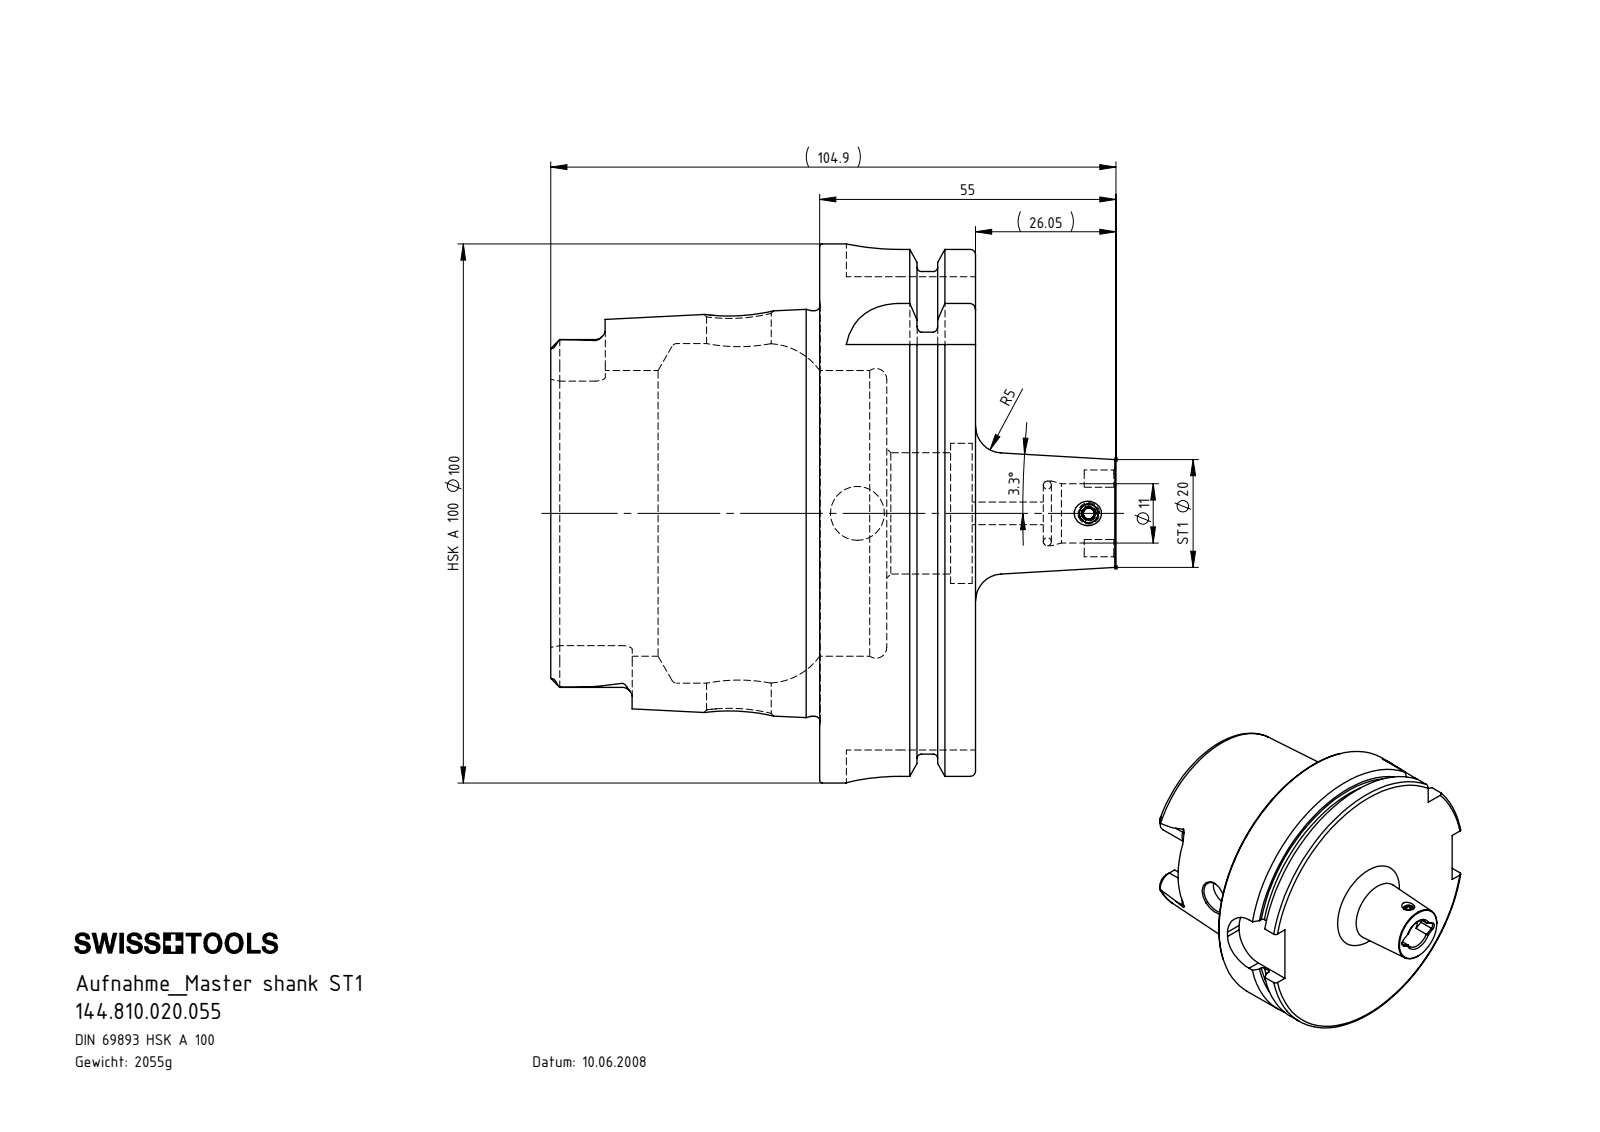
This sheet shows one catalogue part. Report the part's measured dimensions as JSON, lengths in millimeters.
{"part_name": "HA0-ST1.K01.055; DIN 3771 - 9x1.5; HA0-ST1.K01.055_A_Fertigbearbeitung; ST1-ER1.001.005_A", "step_written_by": "SolidWorks 2015 (CONFIG_CONTROL_DESIGN)", "units": "millimeters", "bodies": {"solids": 3, "faces": 202, "planar": 57, "cylindrical": 57, "other": 88}, "overall_size": [104.9, 100, 100], "volume_mm3": 260677, "surface_area_mm2": 52045, "round_holes": [[12, 2], [3.5, 1], [4.2, 1], [10, 1], [11, 1], [22.5, 1], [26, 1], [53, 1], [63, 1]], "round_bosses_or_shafts": [[100, 1], [91.95, 1], [75.26, 1], [20, 1], [4, 1]], "partial_cylinders_radius": [[1.9, 6], [4.88, 4], [10, 4], [1.3, 2]], "face_to_face_distances": [28.95, 12.45, 16.5, 49.9, 62.35, 78.85, 78.2, 28.3, 15.85, 0.65], "hole_center_spacings": [42.95]}
